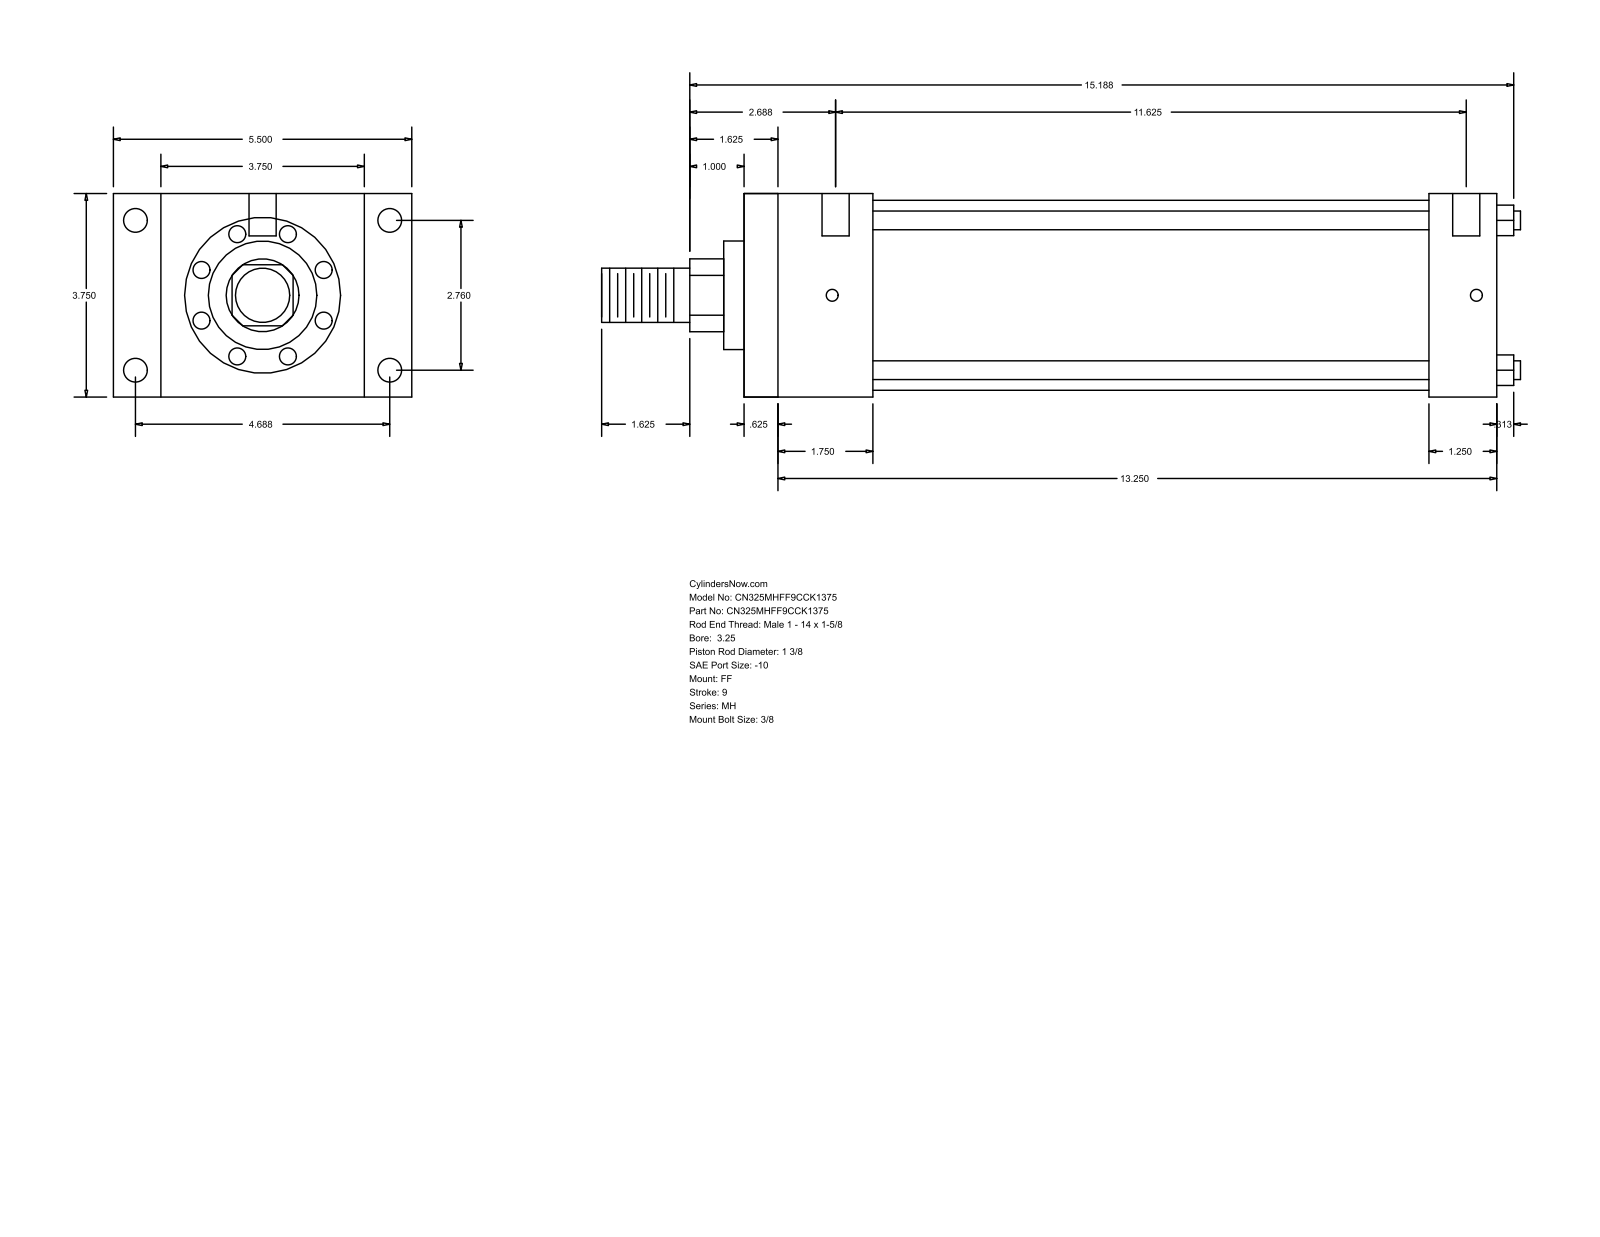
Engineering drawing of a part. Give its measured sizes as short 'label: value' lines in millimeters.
name: MH_FF__0325_1.375
written by: GSSL Pune (CONFIG_CONTROL_DESIGN)
unit: mm
bodies: 0 solids, 92 faces (64 planar, 28 cylindrical, 0 other)
size: 430.21 × 139.7 × 95.25
holes: 4× ⌀5.56, 4× ⌀11.13, 2× ⌀12.7
bosses: 4× ⌀8.76, 1× ⌀88.9, 1× ⌀50.8, 1× ⌀34.92, 1× ⌀25.4
rounds: 1× R17.06
face distances: 95.24, 352.42, 15.87, 336.55, 22.23, 117.47, 320.67, 304.8, 31.75, 60.32
hole spacings: 70.1, 119.06, 138.16, 301.63, 1.59, 4.76, 295.28, 296.87
